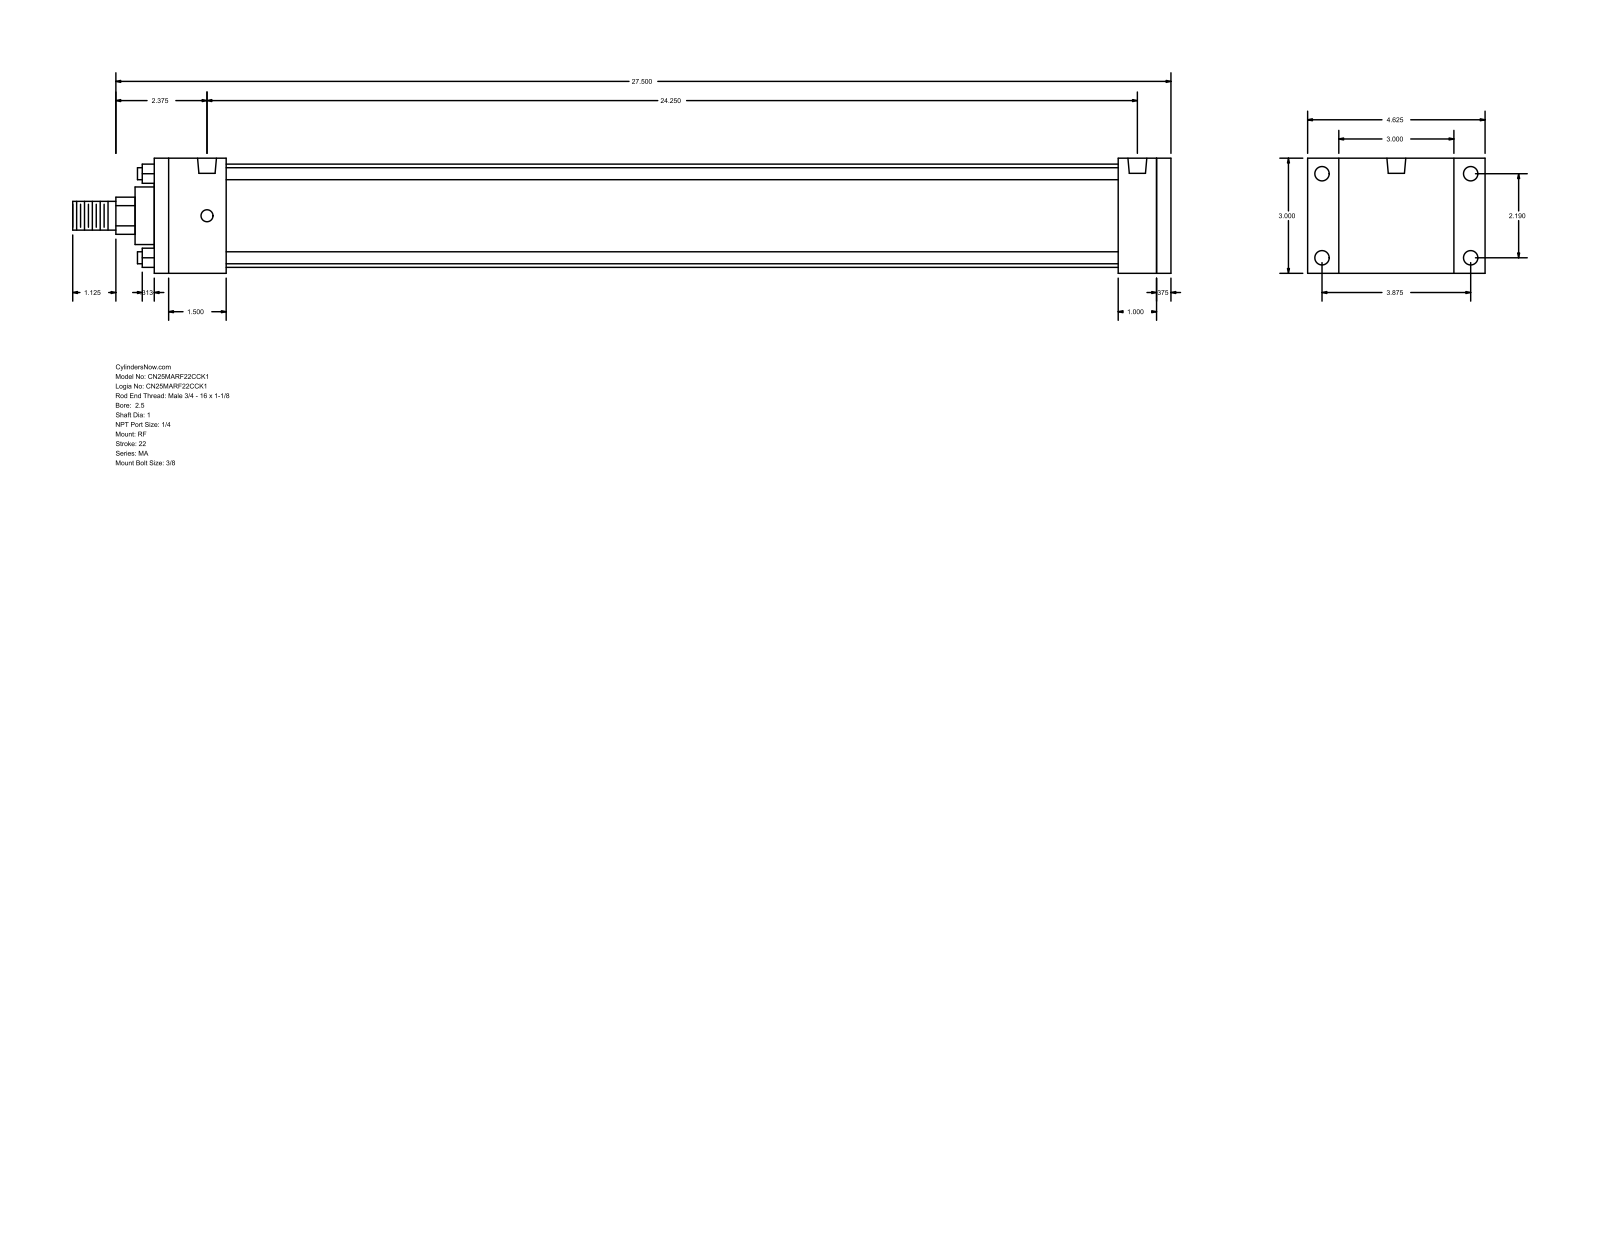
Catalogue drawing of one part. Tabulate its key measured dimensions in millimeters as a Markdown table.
| quantity | value |
| --- | --- |
| part name | MA_RF__0250_1 |
| STEP written by | GSSL Pune (CONFIG_CONTROL_DESIGN) |
| units | millimeters |
| bodies | 0 solids, 92 faces (64 planar, 28 cylindrical, 0 other) |
| overall size | 727.08 × 117.47 × 76.2 |
| round holes (diameter × count) | 7.94 × 4, 9.53 × 4, 12.49 × 2 |
| round bosses / shafts (diameter × count) | 7.94 × 4, 68.33 × 1, 38.1 × 1, 25.4 × 1, 19.05 × 1 |
| partial cylindrical surfaces (radius × count) | 12.29 × 1 |
| main face-to-face distances | 76.2, 673.1, 663.58, 9.52, 25.4, 47.63, 638.18, 590.55, 615.95, 625.47 |
| hole center spacings | 55.62, 98.42, 113.05, 615.94 |
